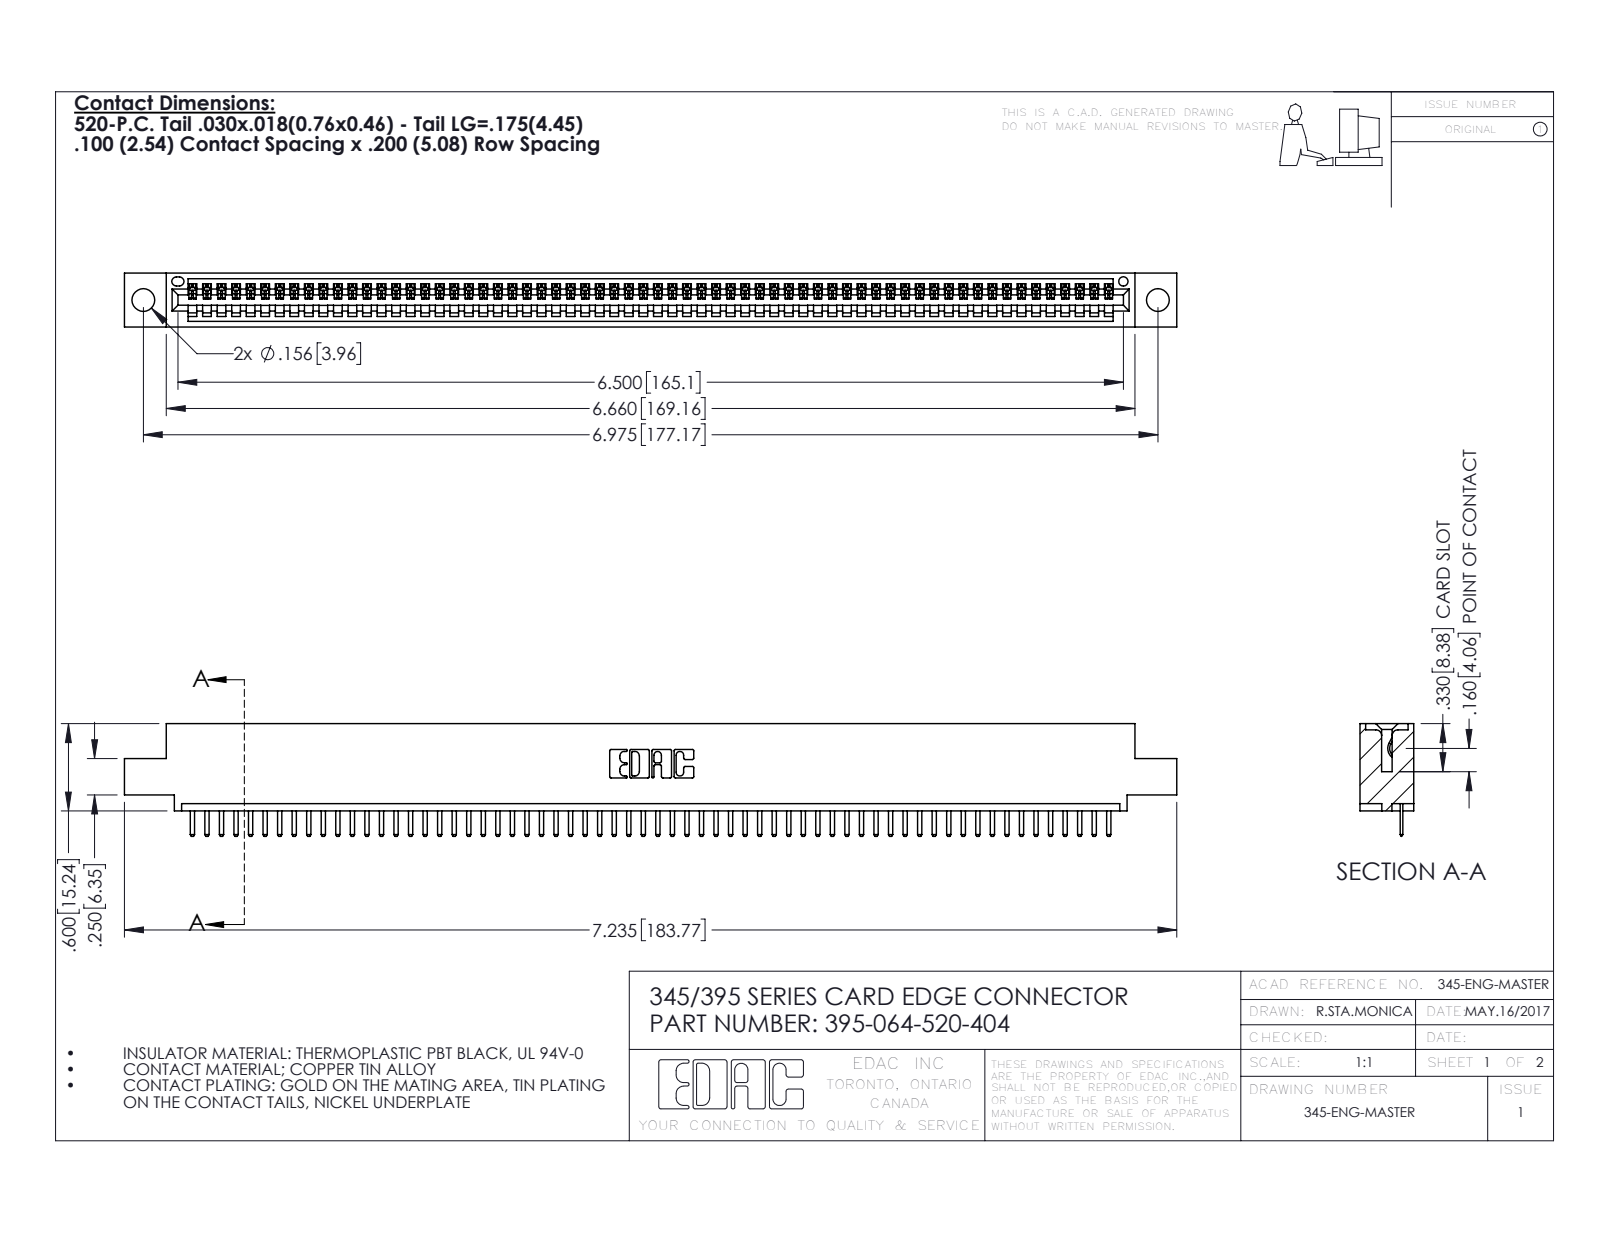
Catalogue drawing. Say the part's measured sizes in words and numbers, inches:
The part is named "345-292-001_345-293-120; 345 Part_0.110 Offset - 0.156 Dia-TH; 395-064-520-404". Its 3-D file was written by "SolidWorks 2016 (CONFIG_CONTROL_DESIGN)". It is 65 solids with 4098 faces: 2772 planar, 1326 cylindrical and 0 other. Overall it measures 7.235 by 0.775 by 0.37 inches. Its volume is 1.055 cubic inches and its surface area 34.97 square inches. Round holes: 2 of diameter 0.156, 1 of diameter 0.064. Partial cylindrical surfaces (rounded edges, fillets, slot ends): 130 of radius 0.01, 128 of radius 0.006, 22 of radius 0.01, 6 of radius 0.007, 6 of radius 0.031, 3 of radius 0.026, 2 of radius 0.031, 2 of radius 0.04. The main face-to-face distances are 0.298, 0.072, 0.37, 0.2, 0.098, 0.272, 0.025, 0.225, 0.072, 0.149. The hole center spacings are 0.27, 6.739, 6.975.
